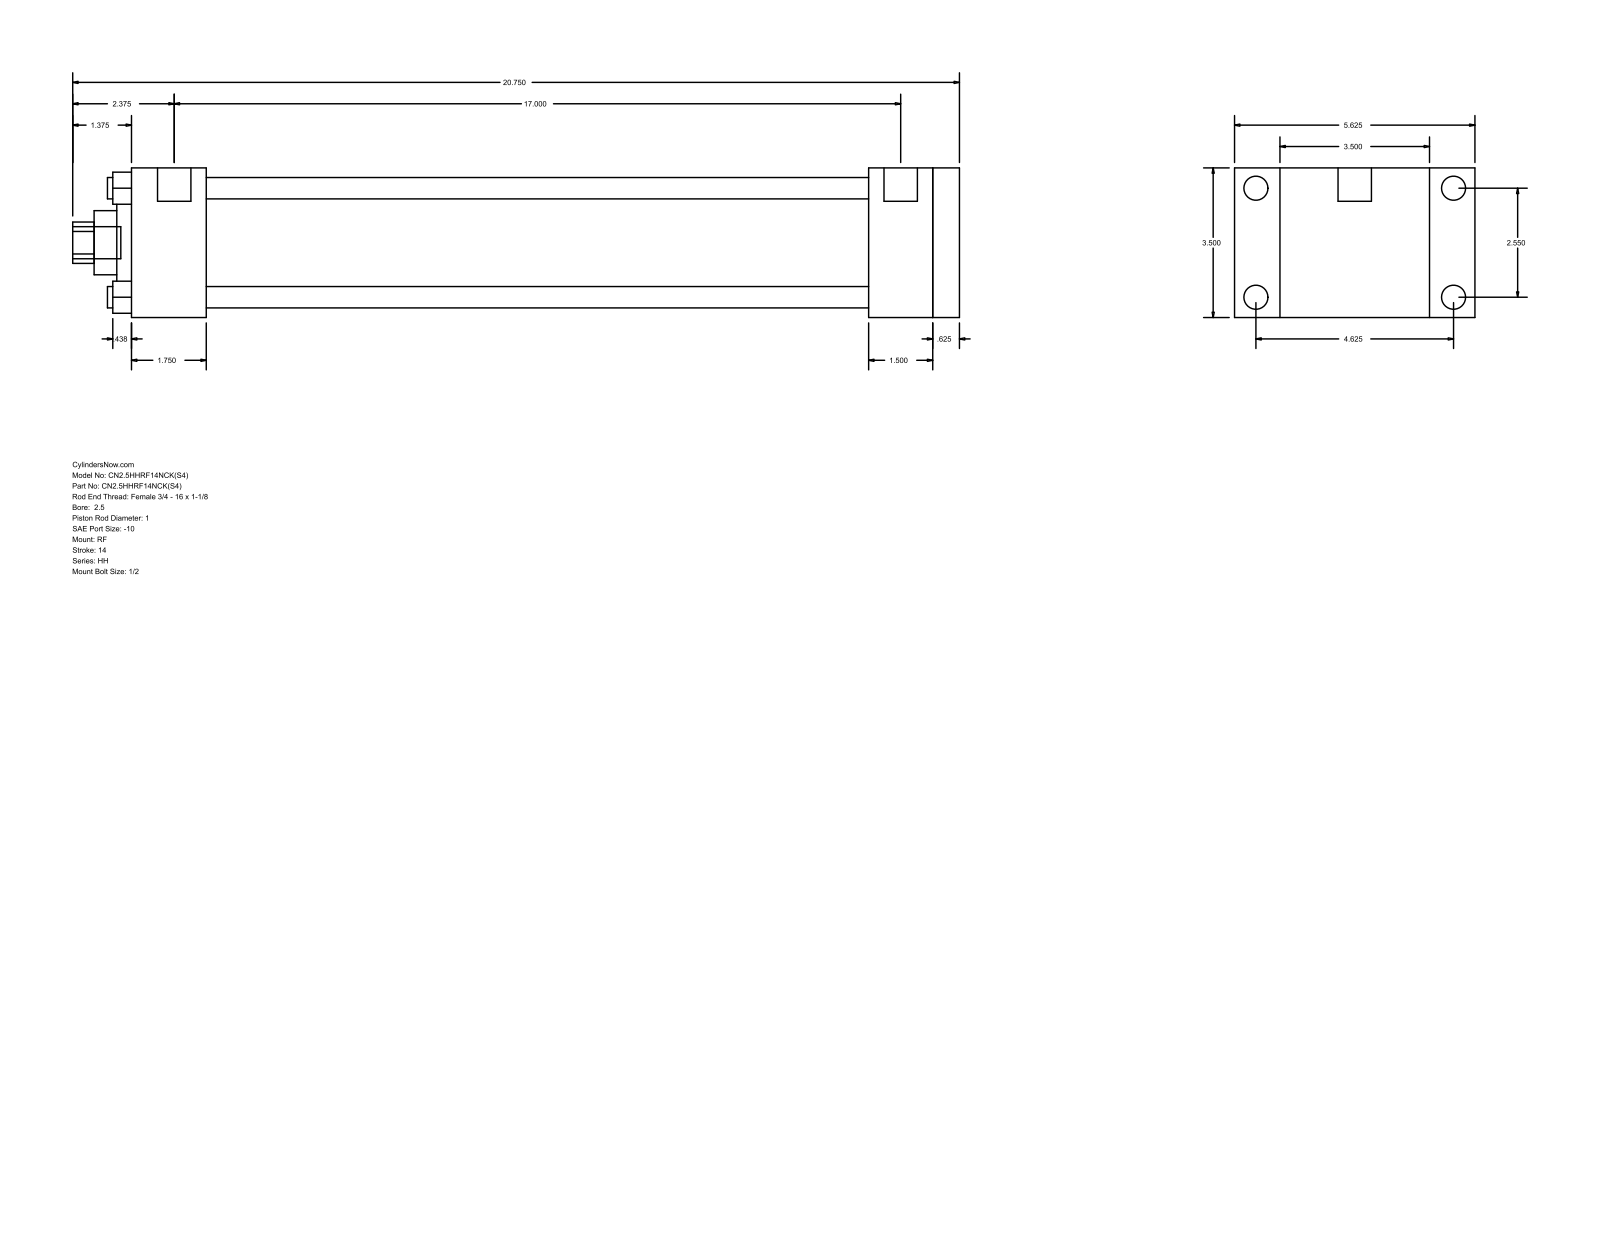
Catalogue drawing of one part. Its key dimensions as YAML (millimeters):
part_name: "HH_RF__0250_1"
step_written_by: "GSSL Pune (CONFIG_CONTROL_DESIGN)"
units: millimeters
bodies: {solids: 0, faces: 94, planar: 65, cylindrical: 29, other: 0}
overall_size: [527.05, 142.88, 88.9]
round_holes:
  - {diameter: 12.7, count: 4}
  - {diameter: 25.4, count: 1}
  - {diameter: 38.1, count: 1}
  - {diameter: 60.33, count: 1}
  - {diameter: 73.03, count: 1}
round_bosses_or_shafts:
  - {diameter: 14.3, count: 4}
  - {diameter: 5.56, count: 4}
  - {diameter: 19.84, count: 2}
  - {diameter: 19.05, count: 1}
partial_cylinders:
  - {radius: 12.29, count: 1}
face_to_face_distances: [88.9, 15.87, 476.26, 492.13, 44.46, 431.8, 447.67, 438.15, 393.69, 38.11]
hole_center_spacings: [45.79, 64.76, 91.58]
